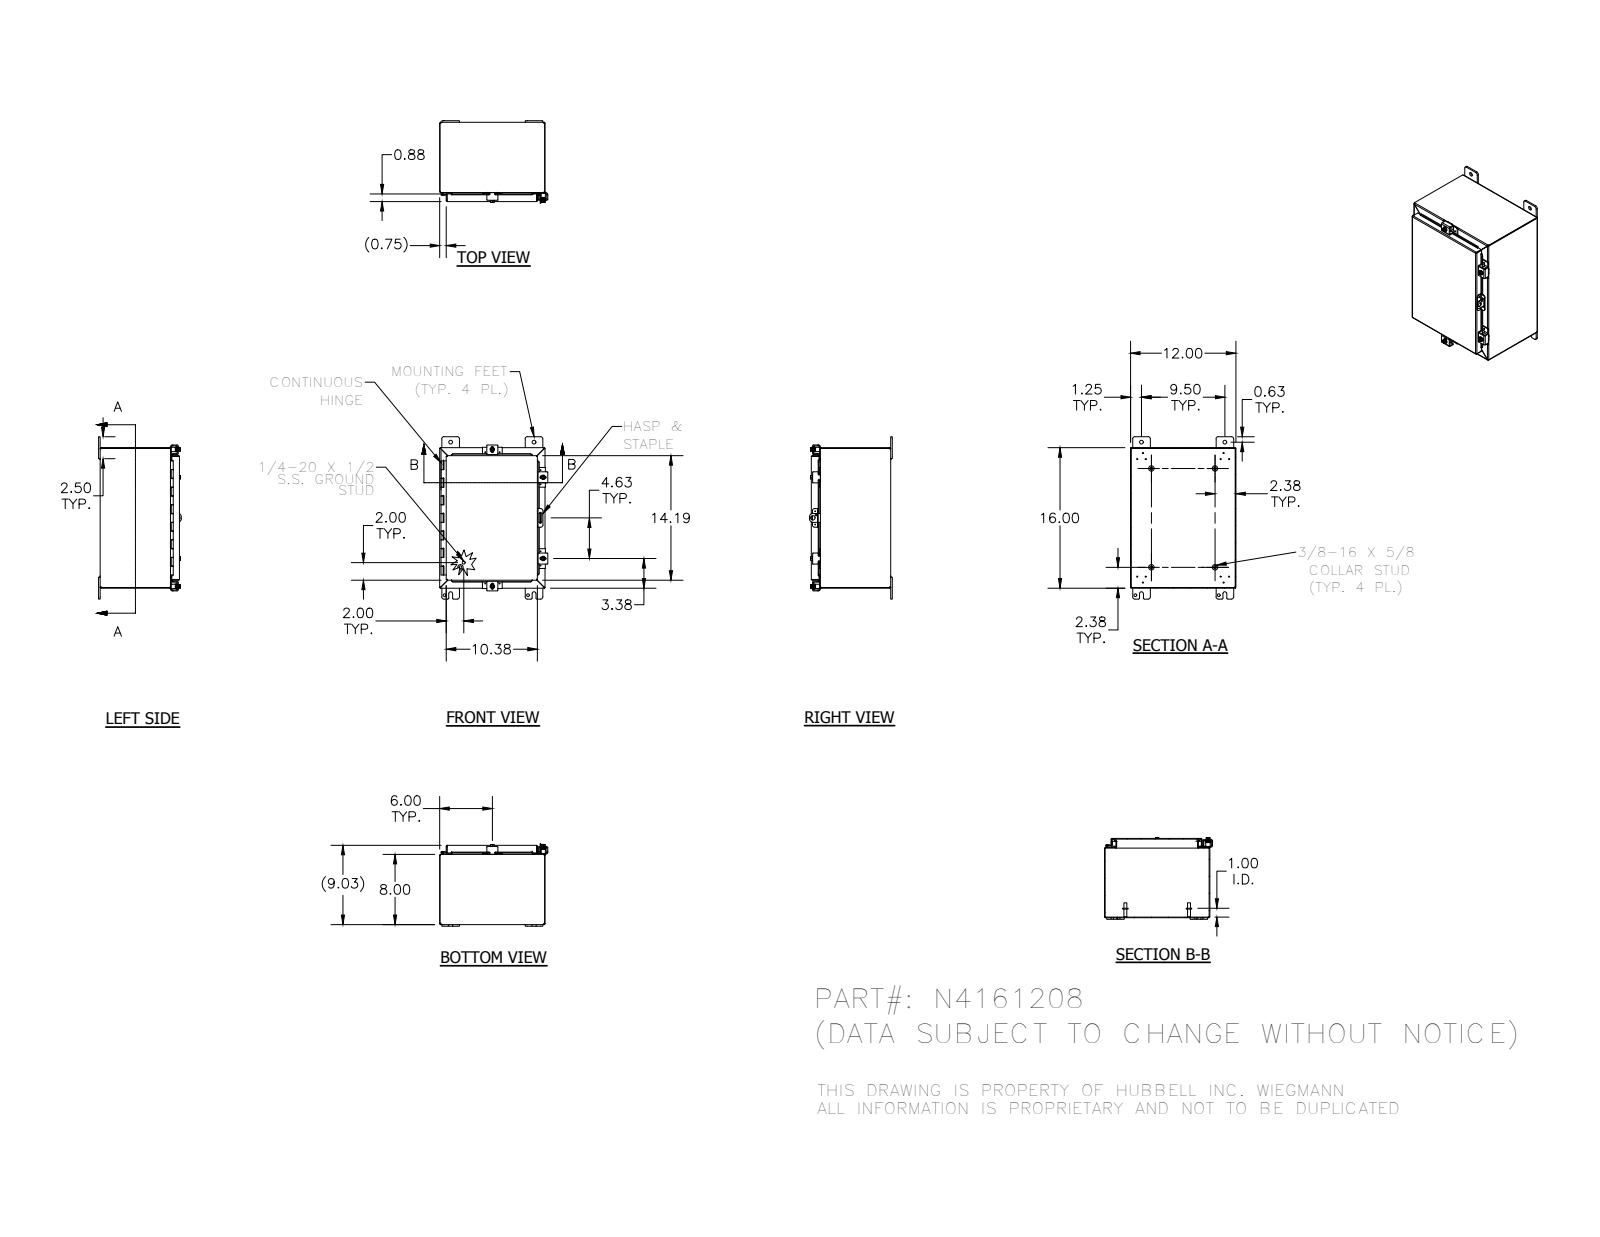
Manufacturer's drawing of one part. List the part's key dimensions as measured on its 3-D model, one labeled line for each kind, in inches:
Part name (STEP PRODUCT): 328103_1; 328103P-1_1; 328103L_1; HFW30825-2_1 (+8 more)
STEP written by: SolidWorks 2014 (AUTOMOTIVE_DESIGN)
Units: inches
Bodies: 37 solids, 1568 faces (611 planar, 700 cylindrical, 257 other)
Overall size (bounding box): 18.5 × 12.311 × 9.41
Volume: 82.14 in³ · Surface area: 2 116 in²
Round holes (diameter × count): ⌀0.12 ×12, ⌀0.11 ×11, ⌀0.211 ×4, ⌀0.281 ×4, ⌀0.3 ×4, ⌀0.313 ×4, ⌀0.438 ×4, ⌀0.125 ×1, ⌀0.156 ×1, ⌀0.5 ×1
Round bosses / shafts (diameter × count): ⌀0.25 ×6, ⌀0.625 ×4, ⌀0.52 ×4, ⌀0.5 ×4, ⌀0.35 ×4, ⌀0.33 ×4, ⌀0.115 ×2, ⌀0.337 ×1
Partial cylindrical surfaces — rounded edges, fillets, slot ends (radius × count): R0.03 ×49, R0.125 ×33, R0.062 ×29, R0.25 ×29, R0.031 ×23, R0.105 ×23, R0.063 ×10, R0.07 ×8
Main face-to-face distances: 0.074, 8.959, 11.926, 15.926, 8.885, 9.033, 7.926, 1.033, 12, 11.852
Hole centre spacings: 9.5, 0.876, 0.759, 0.94, 0.969, 1.995, 3.543, 3.78
